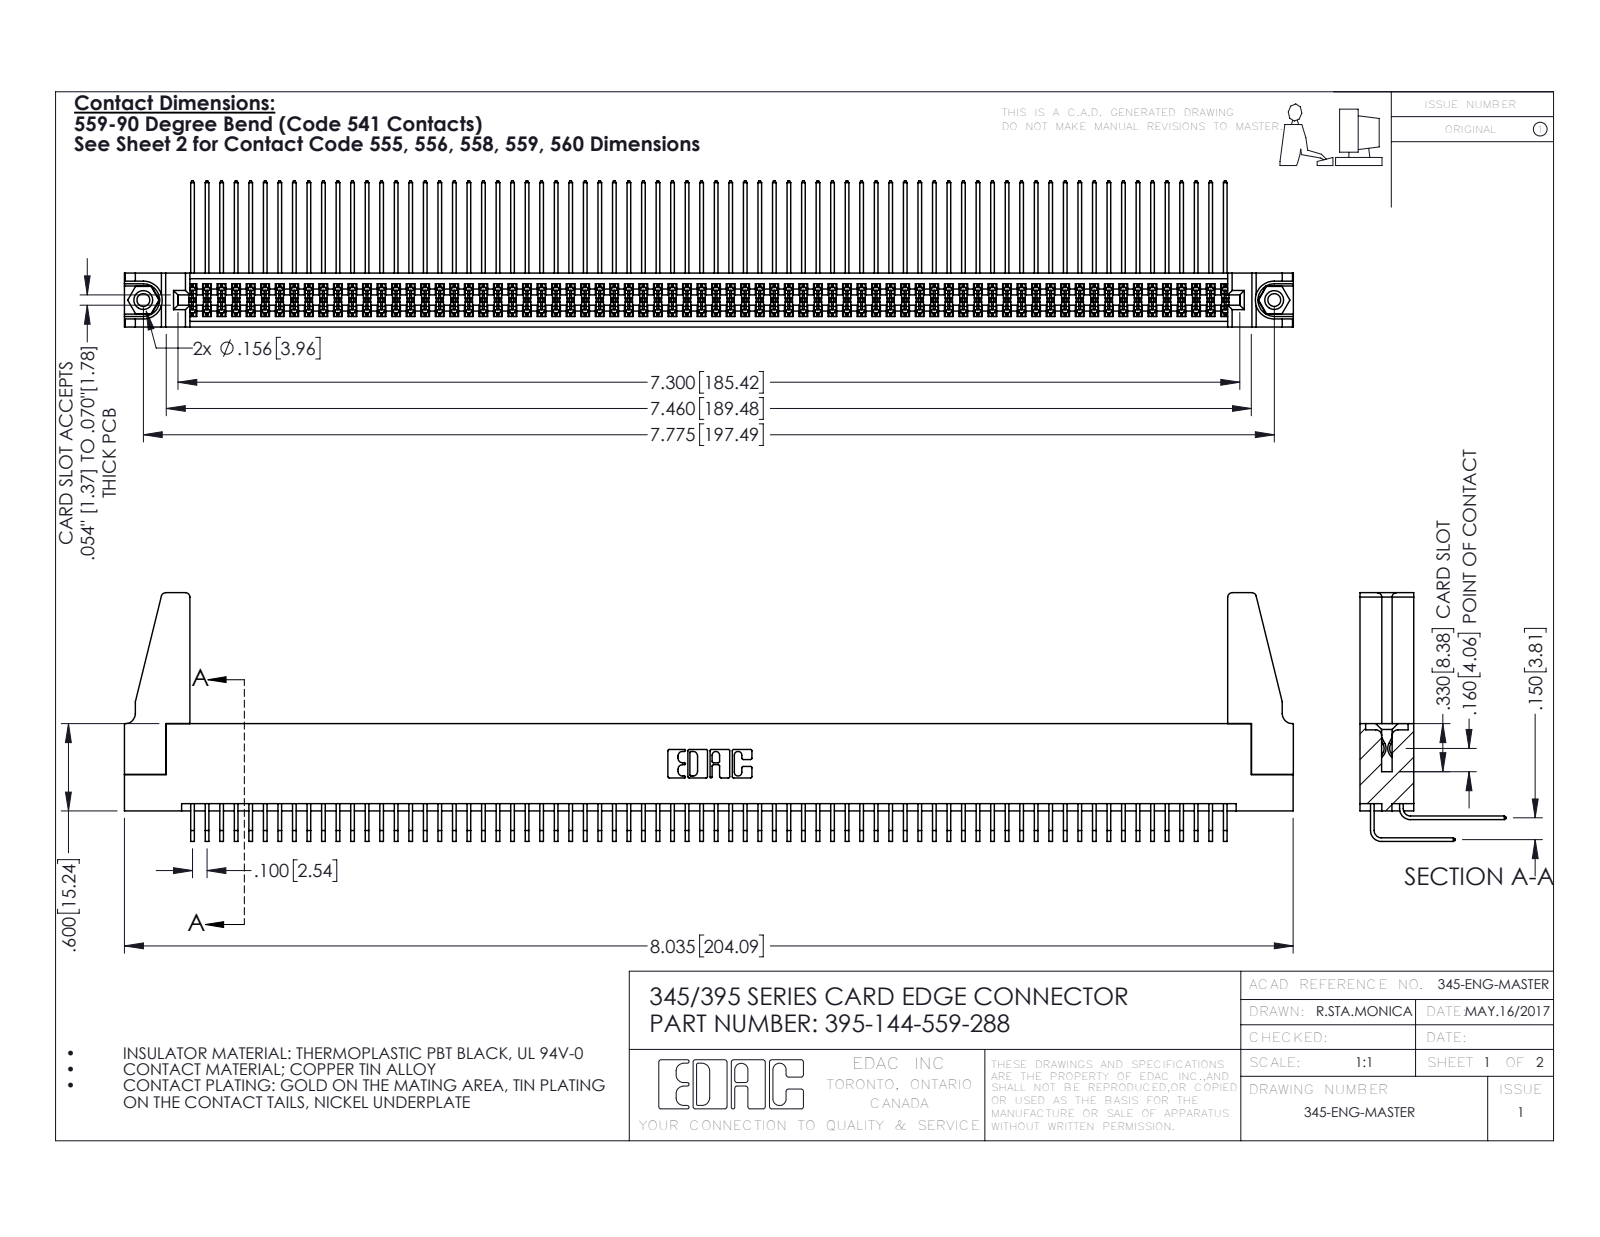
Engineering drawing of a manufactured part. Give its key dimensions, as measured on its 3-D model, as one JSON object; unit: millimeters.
{"part_name": "345-292-001_559 Tail - 2; 345-292-001_558 559 Tail - 1; 345 Part_Flush Mounting Lugs - 0.156 Dia-TH; 345-220-078_345-220-088 (+2 more)", "step_written_by": "SolidWorks 2016 (CONFIG_CONTROL_DESIGN)", "units": "millimeters", "bodies": {"solids": 149, "faces": 7738, "planar": 5192, "cylindrical": 2530, "other": 16}, "overall_size": [204.1, 43.4, 25.5], "volume_mm3": 24190, "surface_area_mm2": 38550, "round_holes": [[2.3, 2], [3.2, 2], [4, 2], [1.6, 1]], "round_bosses_or_shafts": [[3.9, 2]], "partial_cylinders_radius": [[0.2, 217], [0.3, 22], [0.8, 8], [0.2, 6], [0.8, 6], [0.7, 3], [0.4, 2], [0.5, 2]], "face_to_face_distances": [1.8, 7.6, 9.4, 5.1, 2.5, 6.9, 0.6, 5.7, 4.4, 3.8], "hole_center_spacings": [6.9, 191.5, 197.5]}
